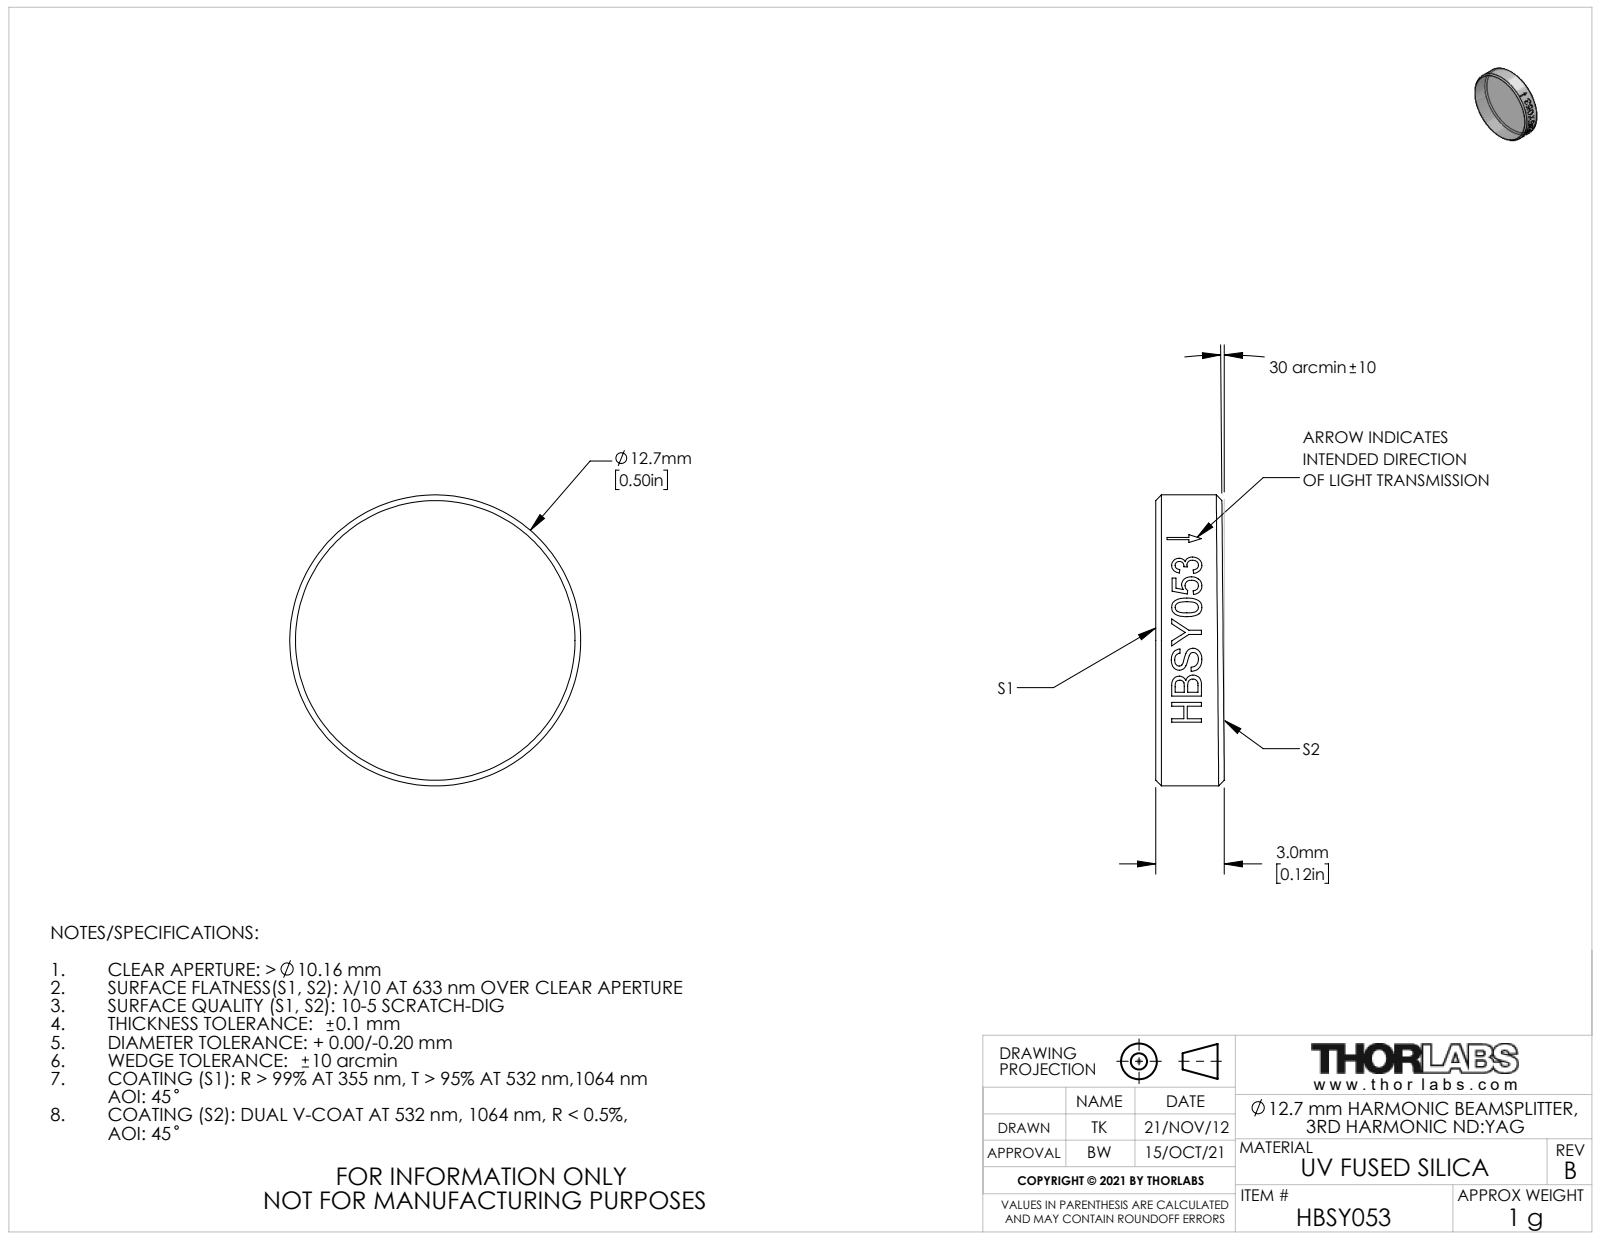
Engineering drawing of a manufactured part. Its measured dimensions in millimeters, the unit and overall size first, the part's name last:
Units: millimetres
Overall size (bounding box): 12.7 × 12.7 × 3
Round bosses / shafts (diameter × count): ⌀12.7 ×1
Volume: 370 mm³ · Surface area: 359 mm²
Bodies: 1 solid, 19 faces (2 planar, 13 cylindrical, 4 other)
Part name (STEP PRODUCT): TTN006420-E0W
STEP written by: SolidWorks 2012 (CONFIG_CONTROL_DESIGN)
